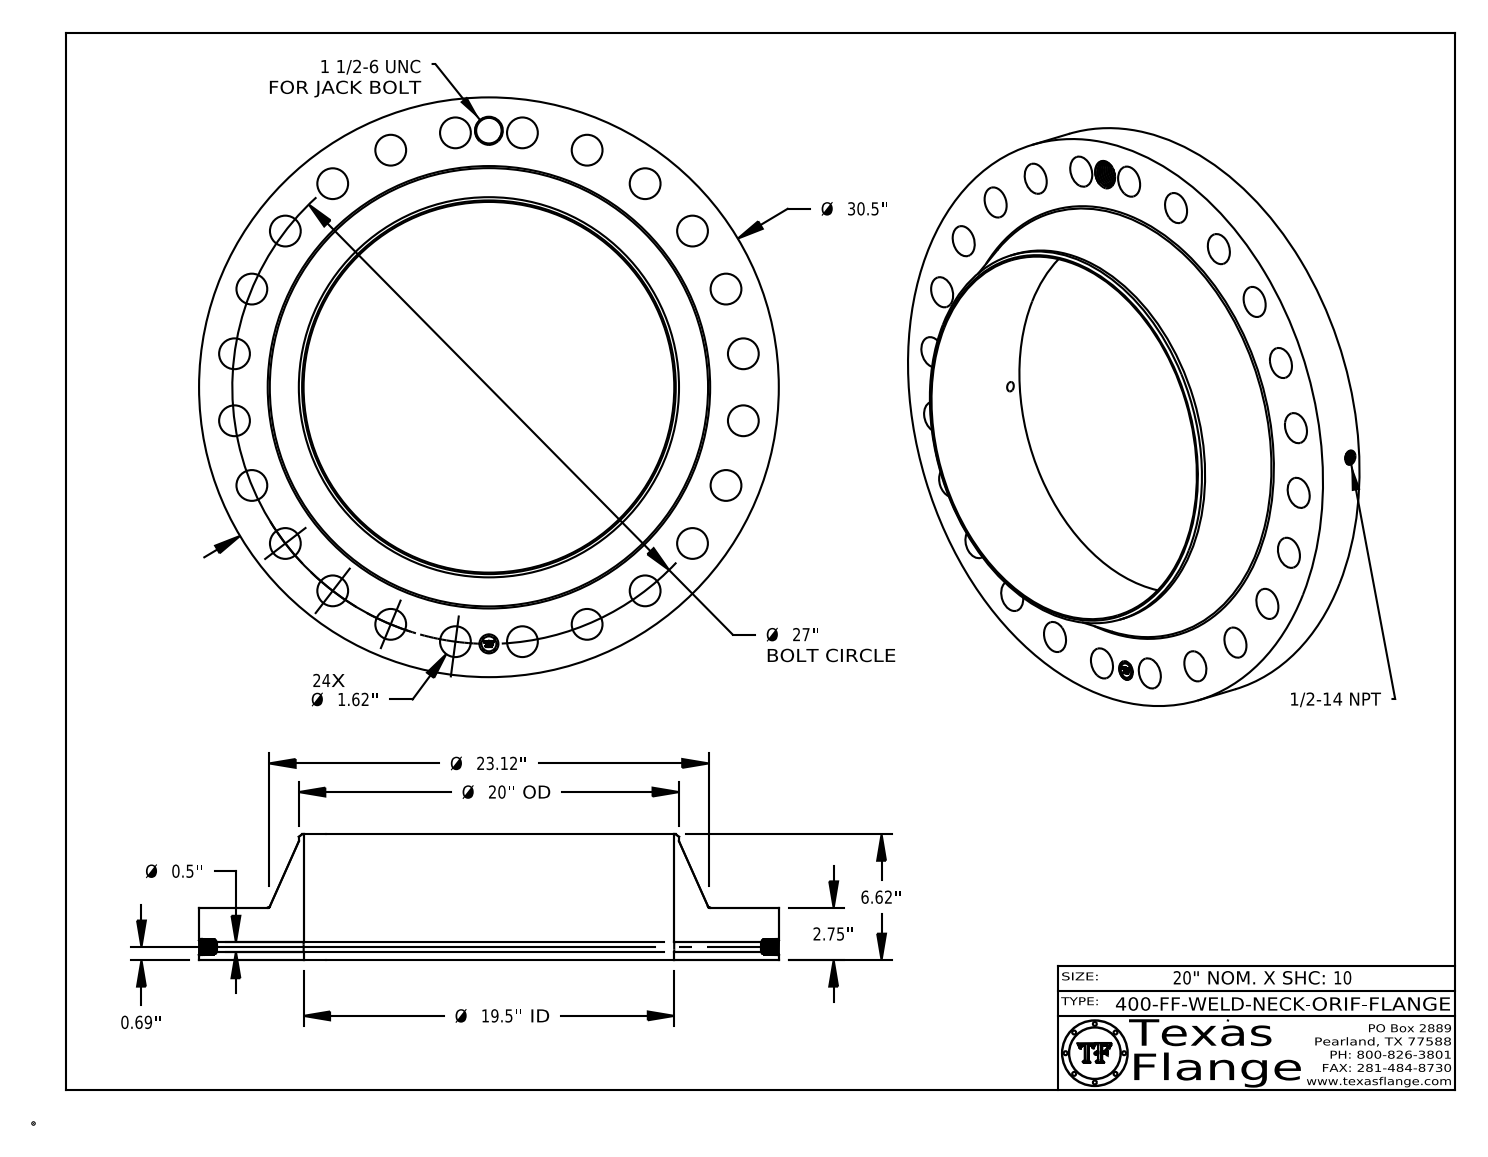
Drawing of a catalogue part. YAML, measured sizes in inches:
part_name: "400-FF-WELD-NECK"
step_written_by: "CATIA V5 STEP AP214 (AUTOMOTIVE_DESIGN)"
units: inches
bodies: {solids: 1, faces: 807, planar: 368, cylindrical: 127, other: 312}
overall_size: [30.5, 30.5, 6.62]
volume: 1285
surface_area: 1975
round_holes:
  - {diameter: 1.62, count: 24}
  - {diameter: 0.5, count: 1}
  - {diameter: 0.672, count: 1}
  - {diameter: 1, count: 1}
  - {diameter: 1.344, count: 1}
  - {diameter: 19.5, count: 1}
round_bosses_or_shafts:
  - {diameter: 0.061, count: 8}
  - {diameter: 30.5, count: 1}
  - {diameter: 20, count: 1}
  - {diameter: 0.788, count: 1}
face_to_face_distances: [2.75, 6.62, 3.87, 2.735, 0.015, 3.885, 0.298, 0.293, 0.054, 0.248]
hole_center_spacings: [13.5, 23.383, 24.945, 21.42, 3.524, 6.988, 19.092, 26.08]
